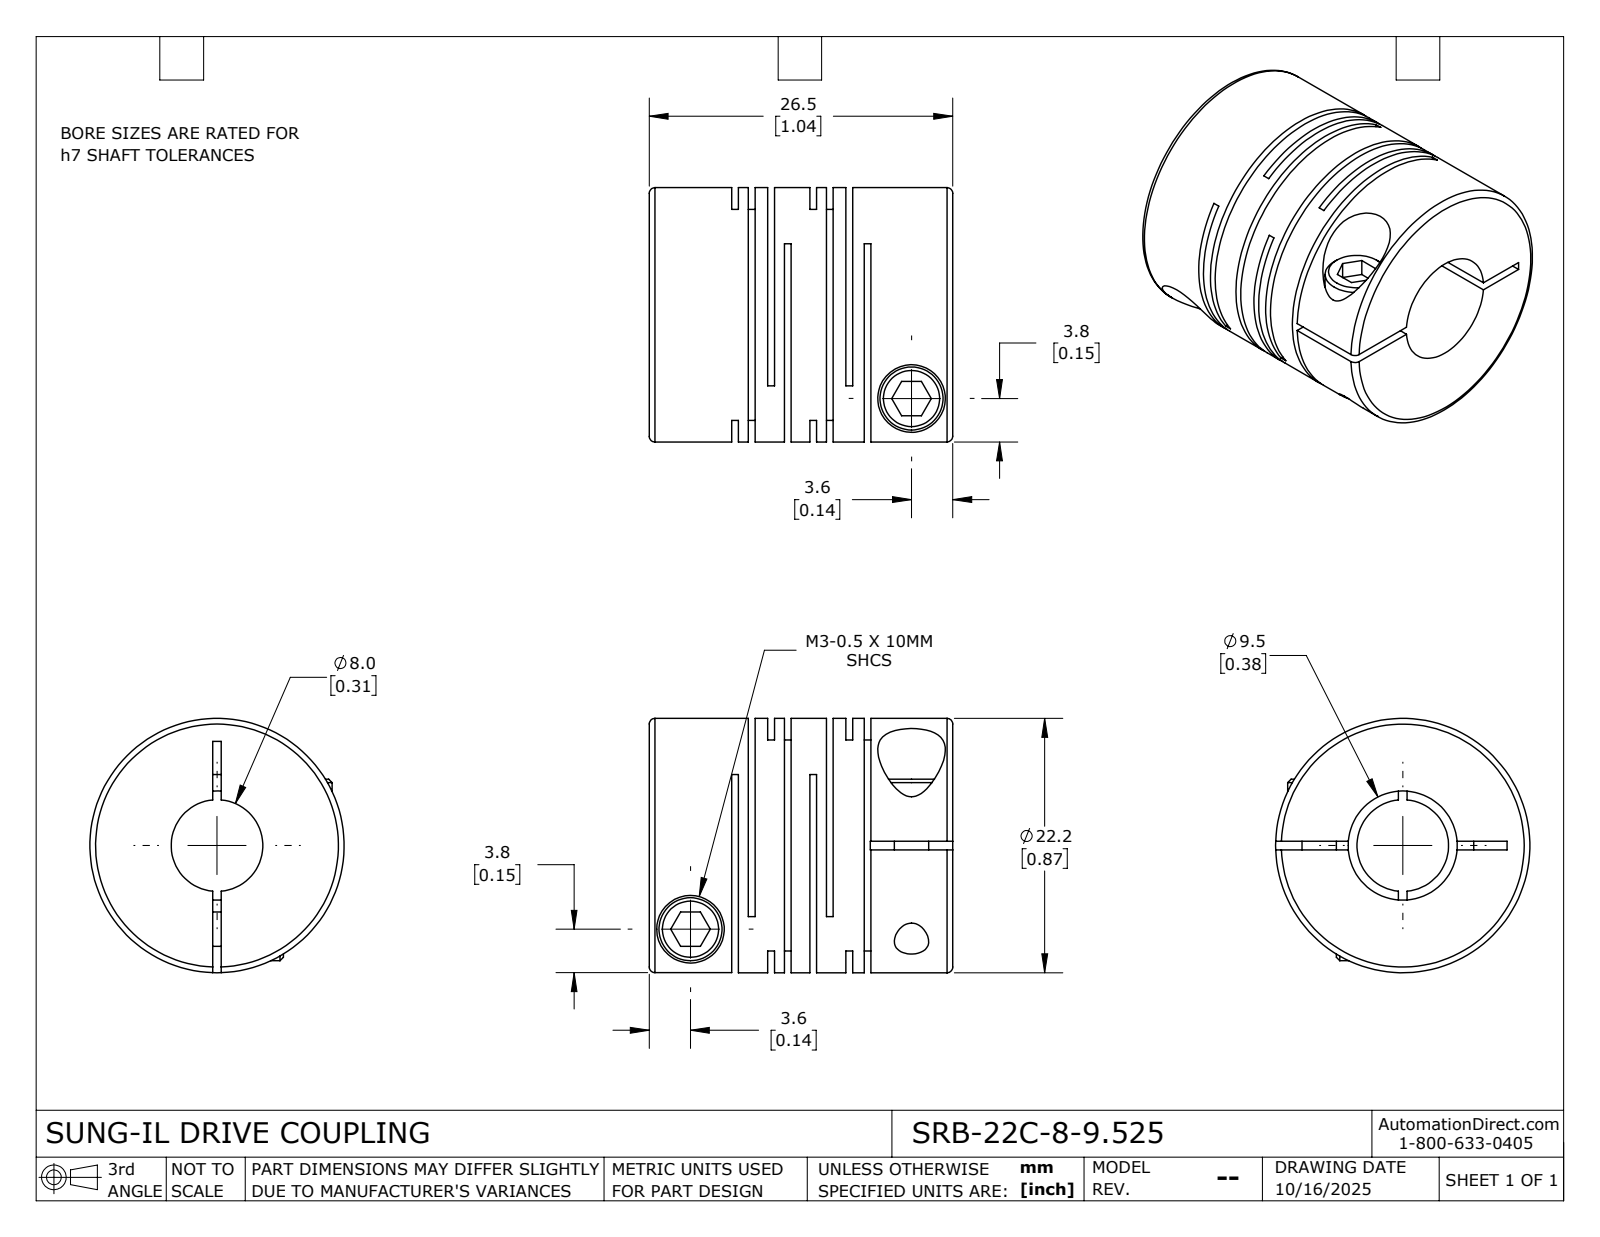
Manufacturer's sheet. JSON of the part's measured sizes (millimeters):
{"part_name": "SRB-22C-8-9.525", "step_written_by": "SolidWorks 2024 (CONFIG_CONTROL_DESIGN)", "units": "millimeters", "bodies": {"solids": 1, "faces": 115, "planar": 60, "cylindrical": 42, "other": 13}, "overall_size": [26.5, 22.2, 22.2], "volume_mm3": 7018, "surface_area_mm2": 7555, "round_holes": [[3, 2], [5.9, 2], [8, 1], [9.53, 1]], "round_bosses_or_shafts": [[5.5, 2], [22.2, 1]], "face_to_face_distances": [0.59, 6.82, 1.45, 3.15, 5.37, 3.67, 1.7, 7.41, 6.23, 2.04]}
